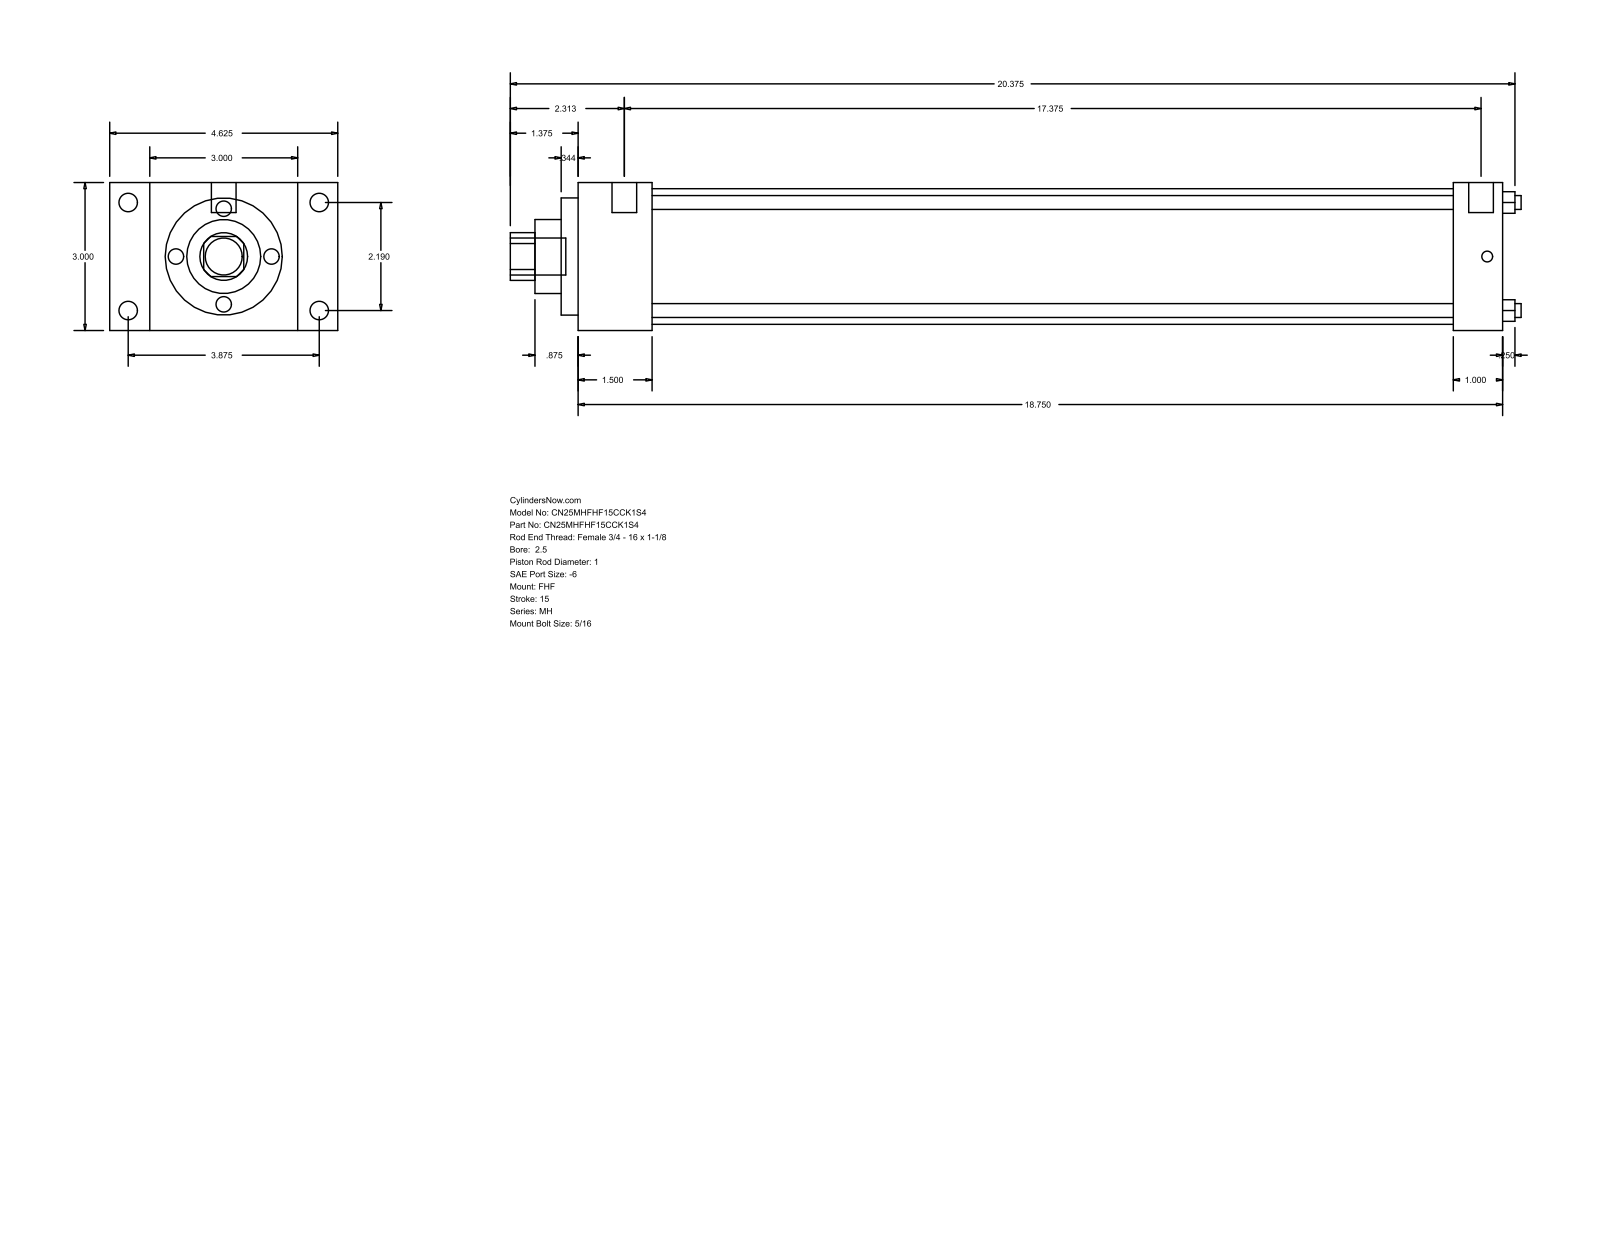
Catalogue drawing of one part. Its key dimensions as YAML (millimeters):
part_name: "MH_FHF__0250_1"
step_written_by: "GSSL Pune (CONFIG_CONTROL_DESIGN)"
units: millimeters
bodies: {solids: 0, faces: 90, planar: 61, cylindrical: 29, other: 0}
overall_size: [520.7, 117.47, 76.2]
round_holes:
  - {diameter: 7.14, count: 4}
  - {diameter: 25.4, count: 1}
  - {diameter: 38.1, count: 1}
  - {diameter: 60.33, count: 1}
  - {diameter: 69.85, count: 1}
round_bosses_or_shafts:
  - {diameter: 9.53, count: 4}
  - {diameter: 5.56, count: 4}
  - {diameter: 12.7, count: 2}
  - {diameter: 19.05, count: 1}
partial_cylinders:
  - {radius: 12.29, count: 1}
face_to_face_distances: [76.2, 476.26, 38.11, 438.15, 20.64, 96.84, 117.48, 450.85, 412.74, 25.41]
hole_center_spacings: [39.33, 55.62, 78.66]
